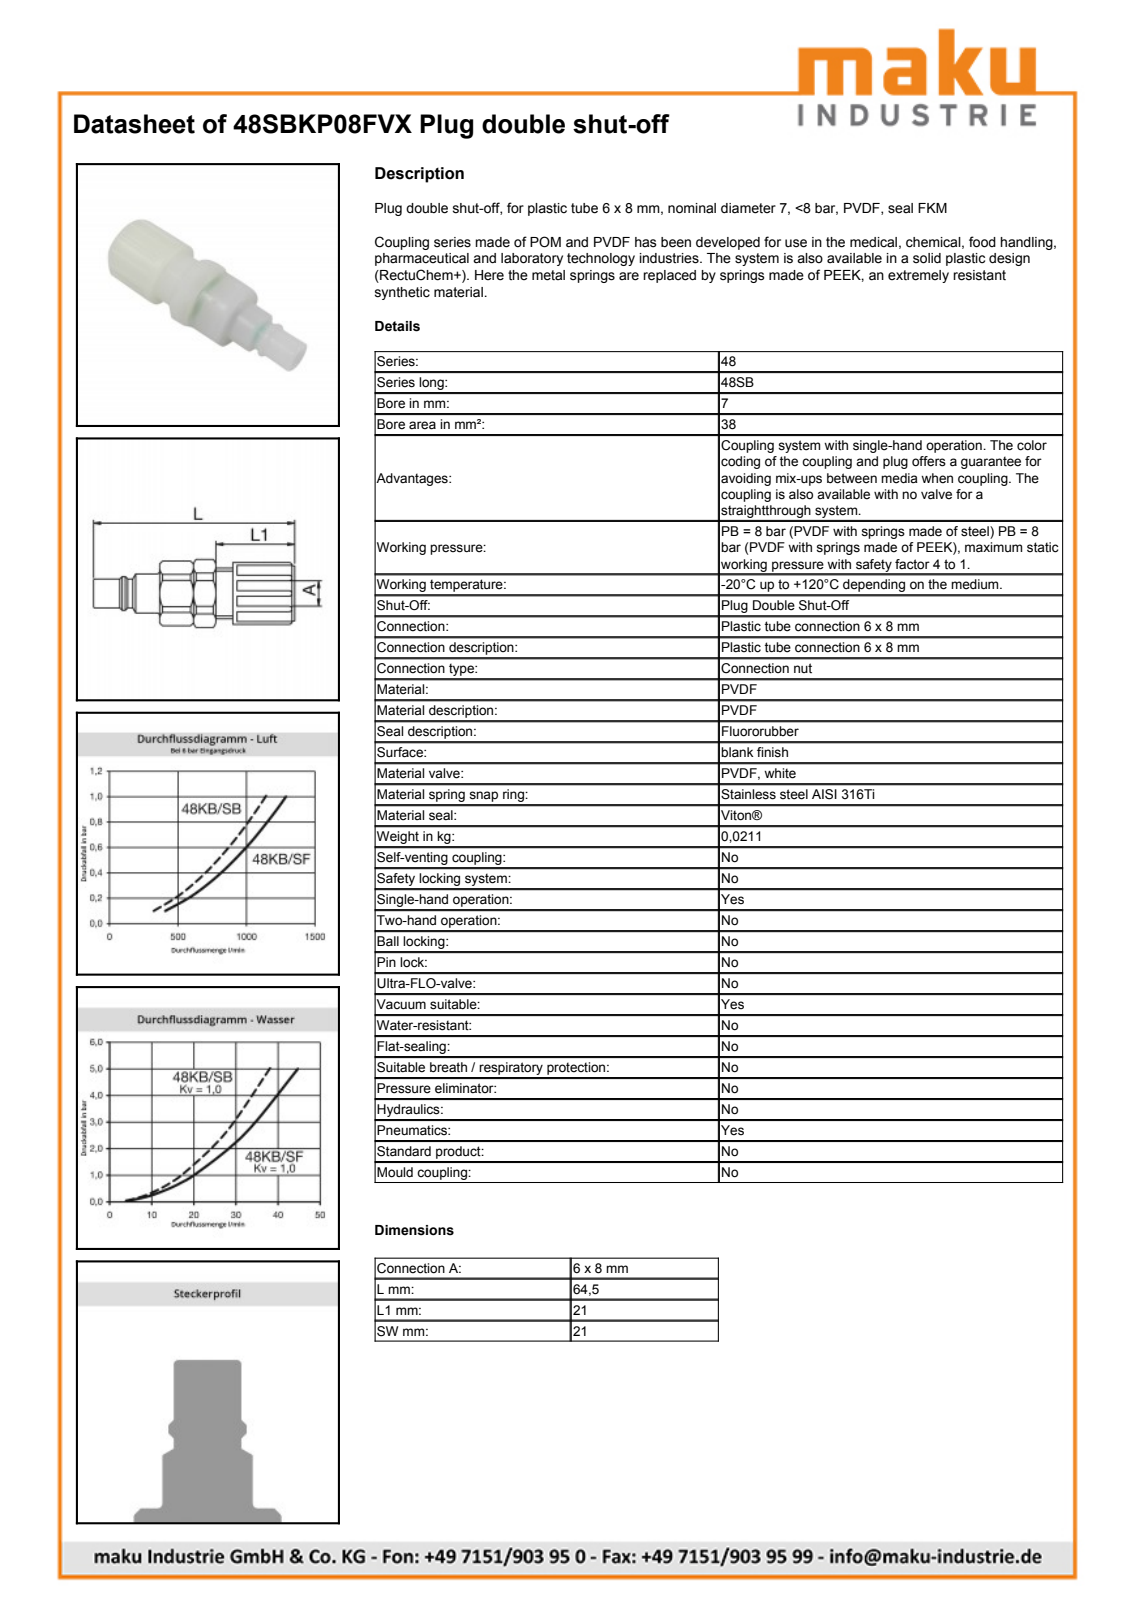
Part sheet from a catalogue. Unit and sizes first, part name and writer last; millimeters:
Units: millimetres
Overall size (bounding box): 67.7 × 24.19 × 23.08
Round bosses / shafts (diameter × count): ⌀22.7 ×1, ⌀18 ×1, ⌀13.9 ×1, ⌀12 ×1, ⌀10.3 ×1
Partial cylindrical surfaces — rounded edges, fillets, slot ends (radius × count): R11.05 ×1, R11.5 ×1, R12.1 ×1
Main face-to-face distances: 21, 22, 20, 5, 25, 19.2, 24.2, 44.2, 21.98, 23.5
Volume: 19 265 mm³ · Surface area: 5 093 mm²
Bodies: 1 solid, 114 faces (59 planar, 30 cylindrical, 25 other)
Part name (STEP PRODUCT): D106269
STEP written by: Autodesk Inventor 2013 (AUTOMOTIVE_DESIGN)
